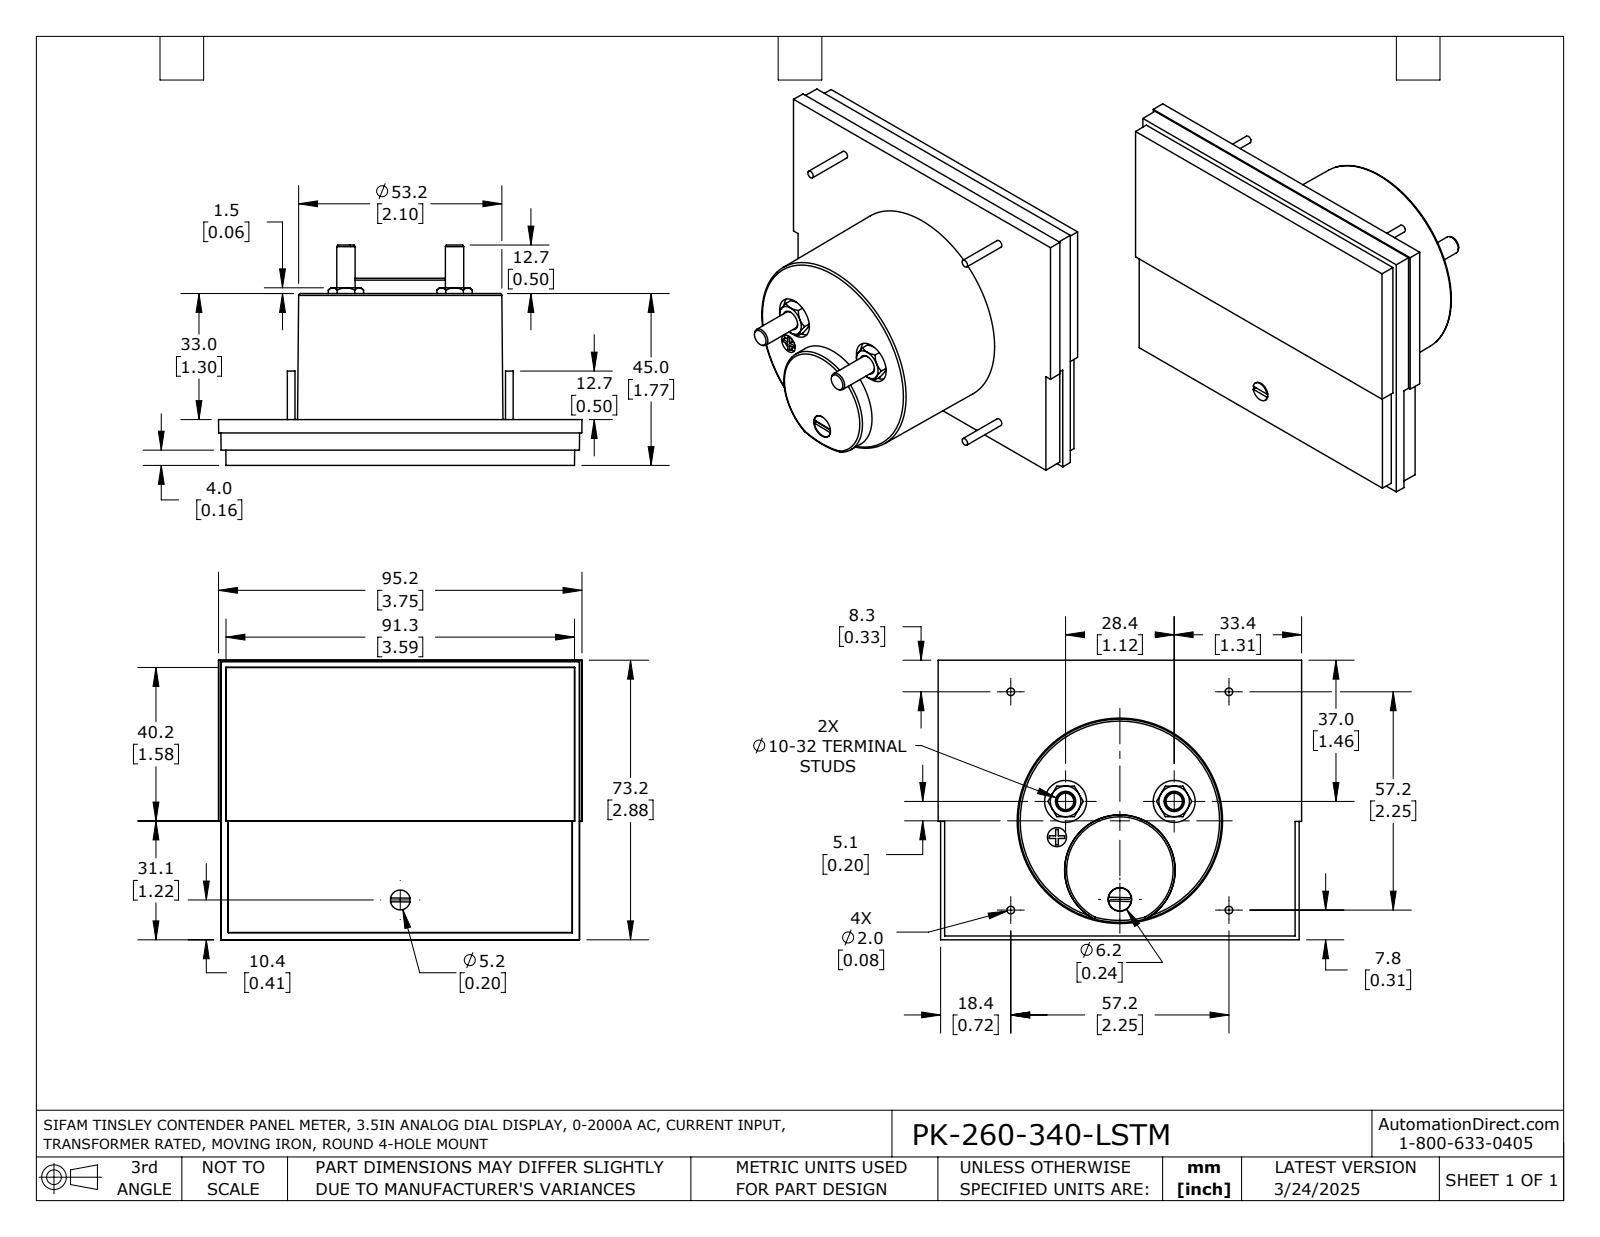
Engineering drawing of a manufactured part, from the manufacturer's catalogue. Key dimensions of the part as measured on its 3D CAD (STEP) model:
Part name (STEP PRODUCT): PK-260-340-LSTM
STEP written by: SolidWorks 2021 (AUTOMOTIVE_DESIGN)
Units: inches
Bodies: 1 solid, 163 faces (76 planar, 31 cylindrical, 56 other)
Overall size (bounding box): 3.748 × 2.882 × 2.272
Volume: 9.446 in³ · Surface area: 38.39 in²
Round holes (diameter × count): ⌀0.433 ×2, ⌀0.197 ×1, ⌀0.244 ×1
Round bosses / shafts (diameter × count): ⌀0.079 ×4, ⌀0.189 ×2, ⌀0.236 ×1, ⌀0.205 ×1
Partial cylindrical surfaces — rounded edges, fillets, slot ends (radius × count): R0.1 ×1
Main face-to-face distances: 0.472, 0.03, 0.443, 1.772, 1.299, 1.742, 0.157, 0.073, 0.315, 1.457
Hole centre spacings: 1.155, 0.379, 0.912, 1.12, 1.263
